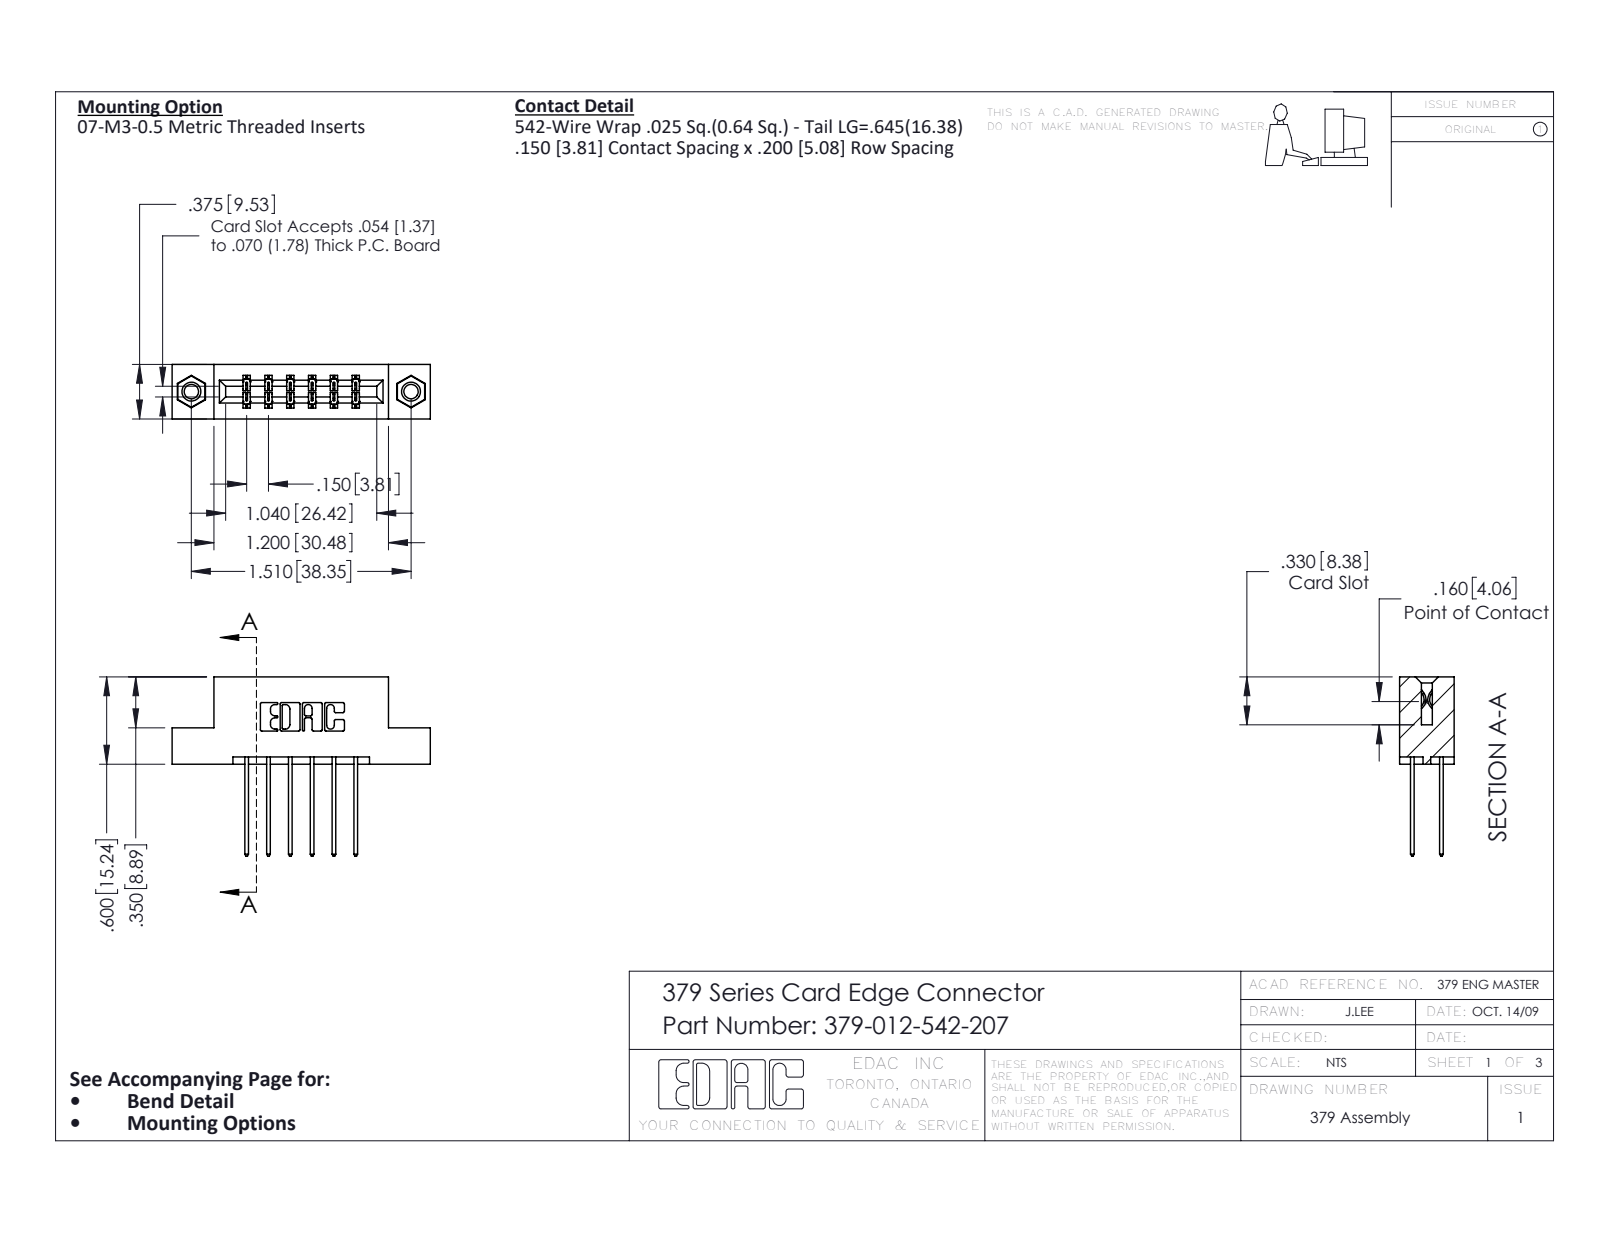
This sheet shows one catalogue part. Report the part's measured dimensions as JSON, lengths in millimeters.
{"part_name": "345-250-001_345-250-005-103; 379-012-542-207; 379 Part_Flush - .156 Dia - TI; 345-292-001_345-293-142", "step_written_by": "SolidWorks 2016 (CONFIG_CONTROL_DESIGN)", "units": "millimeters", "bodies": {"solids": 15, "faces": 798, "planar": 534, "cylindrical": 248, "other": 16}, "overall_size": [45.1, 31.3, 9.5], "volume_mm3": 4390, "surface_area_mm2": 4915, "round_holes": [[2.5, 2], [3.2, 2], [4, 2]], "round_bosses_or_shafts": [[3.9, 2]], "partial_cylinders_radius": [[0.3, 22], [0.2, 18], [0.3, 12], [0.2, 6], [0.8, 6], [0.7, 3], [0.4, 2], [0.6, 2]], "face_to_face_distances": [7.6, 5.1, 3.8, 2.5, 9.5, 1.3, 1.9, 6.4, 8.9, 14], "hole_center_spacings": [38.4]}
